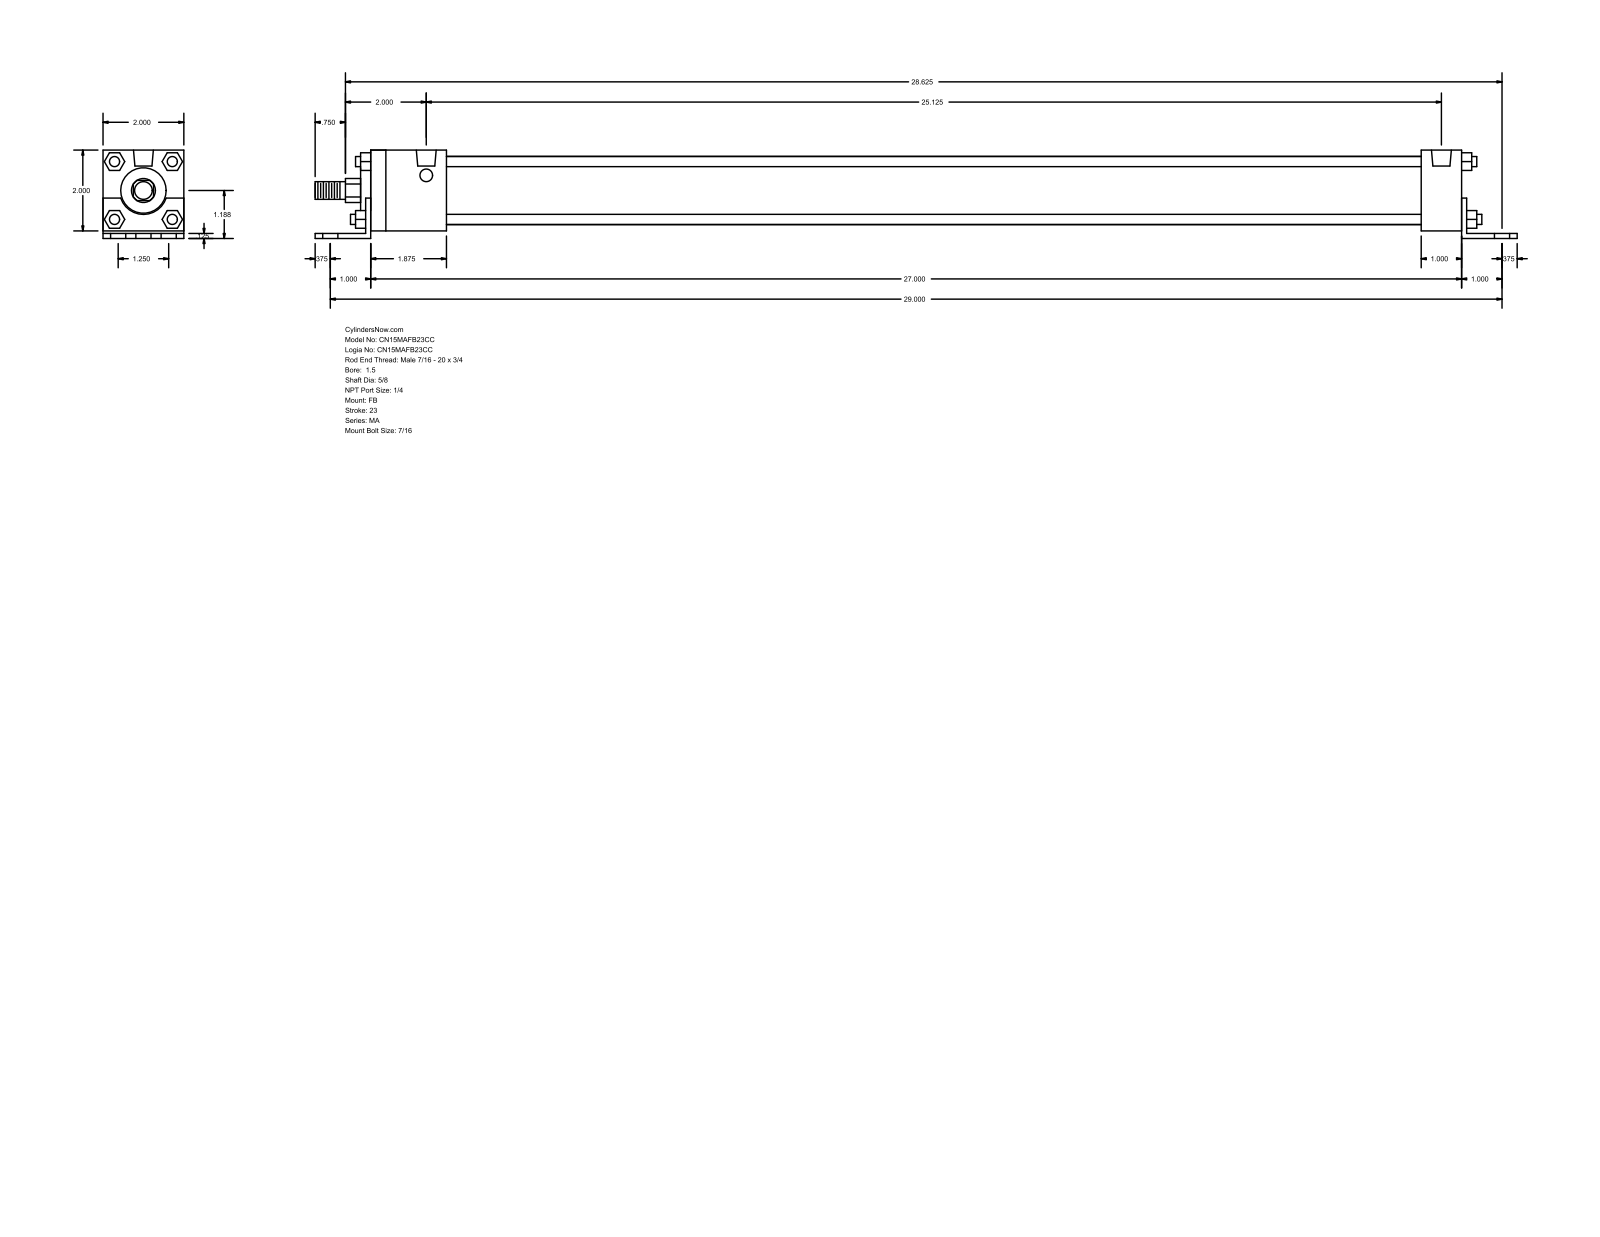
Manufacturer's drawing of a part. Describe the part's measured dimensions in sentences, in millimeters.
The part is named "MA_FB__0150_0.625". Its 3-D file was written by "GSSL Pune (CONFIG_CONTROL_DESIGN)". It is 0 solids with 140 faces: 105 planar, 35 cylindrical and 0 other. Overall it measures 755.65 by 55.56 by 50.8 millimeters. Round holes: 6 of diameter 11.11, 4 of diameter 7.94, 2 of diameter 12.49. Round bosses or shafts: 4 of diameter 6.35, 1 of diameter 42.93, 1 of diameter 28.57, 1 of diameter 15.88, 1 of diameter 11.11. Partial cylindrical surfaces (rounded edges, fillets, slot ends): 1 of radius 7.54, 1 of radius 15.05. The main face-to-face distances are 50.8, 3.17, 4.76, 55.56, 1.59, 52.39, 3.18, 25.4, 688.97, 695.32. The hole center spacings are 15.88, 736.78, 736.61, 31.76, 41.28, 62.38, 638.18, 676.47.
